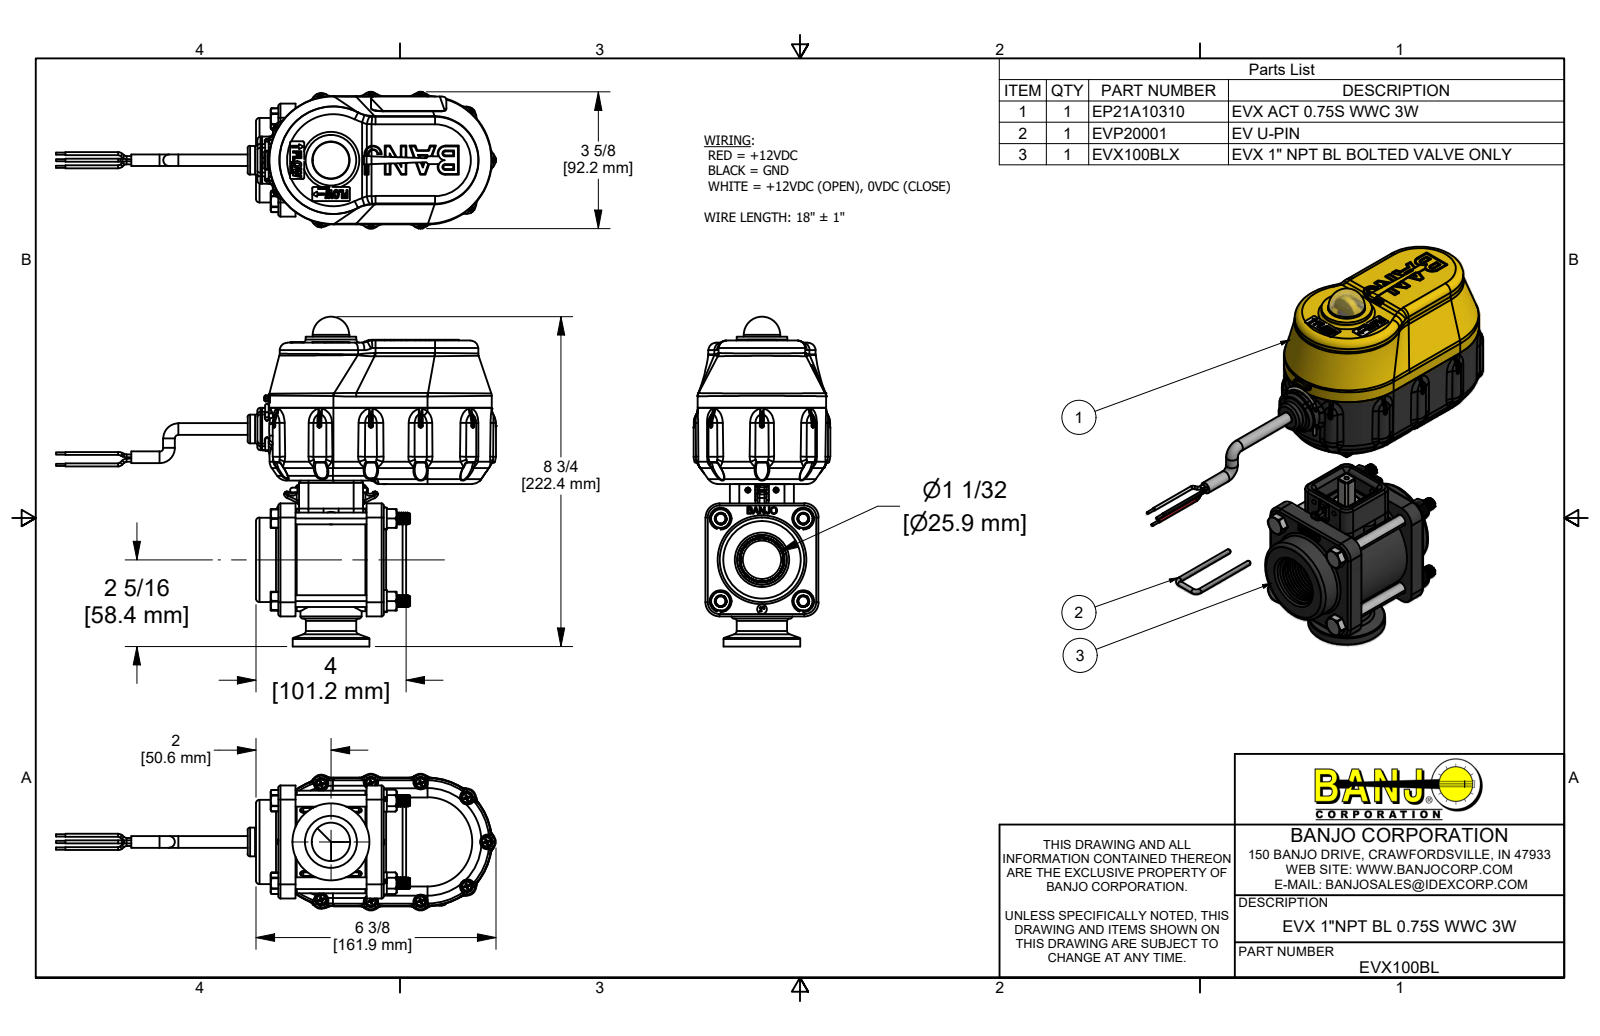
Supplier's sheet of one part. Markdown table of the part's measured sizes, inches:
| quantity | value |
| --- | --- |
| part name | EVX100BL; EP21A10310; EP10310; IRF4905 (+8 more) |
| STEP written by | Autodesk Inventor 2019 (AUTOMOTIVE_DESIGN) |
| units | inches |
| bodies | 98 solids, 12079 faces (3277 planar, 3481 cylindrical, 5321 other) |
| overall size | 38.771 × 8.757 × 3.63 |
| volume | 52.6 in³ |
| surface area | 759.6 in² |
| round holes (diameter × count) | 0.095 × 11, 0.15 × 11, 0.08 × 7, 0.107 × 4, 0.126 × 4, 0.136 × 4, 0.148 × 4, 0.15 × 4, 0.17 × 4, 0.252 × 4, 0.322 × 4, 0.35 × 4 |
| round bosses / shafts (diameter × count) | 0.268 × 60, 0.25 × 17, 0.08 × 15, 0.14 × 11, 0.108 × 11, 0.085 × 11, 0.058 × 6, 0.313 × 5 |
| partial cylindrical surfaces (radius × count) | 0.013 × 180, 0.04 × 145, 0.01 × 84, 0.02 × 72, 0.06 × 58, 0.005 × 53, 0.03 × 38, 0.08 × 28 |
| main face-to-face distances | 0.1, 2.565, 0.055, 0.211, 0.06, 0.151, 0.46, 2.345, 0.125, 0.045 |
| hole center spacings | 1.55, 2.192, 2.656, 1.046, 1.513, 1.662, 1.891, 2.69 |
